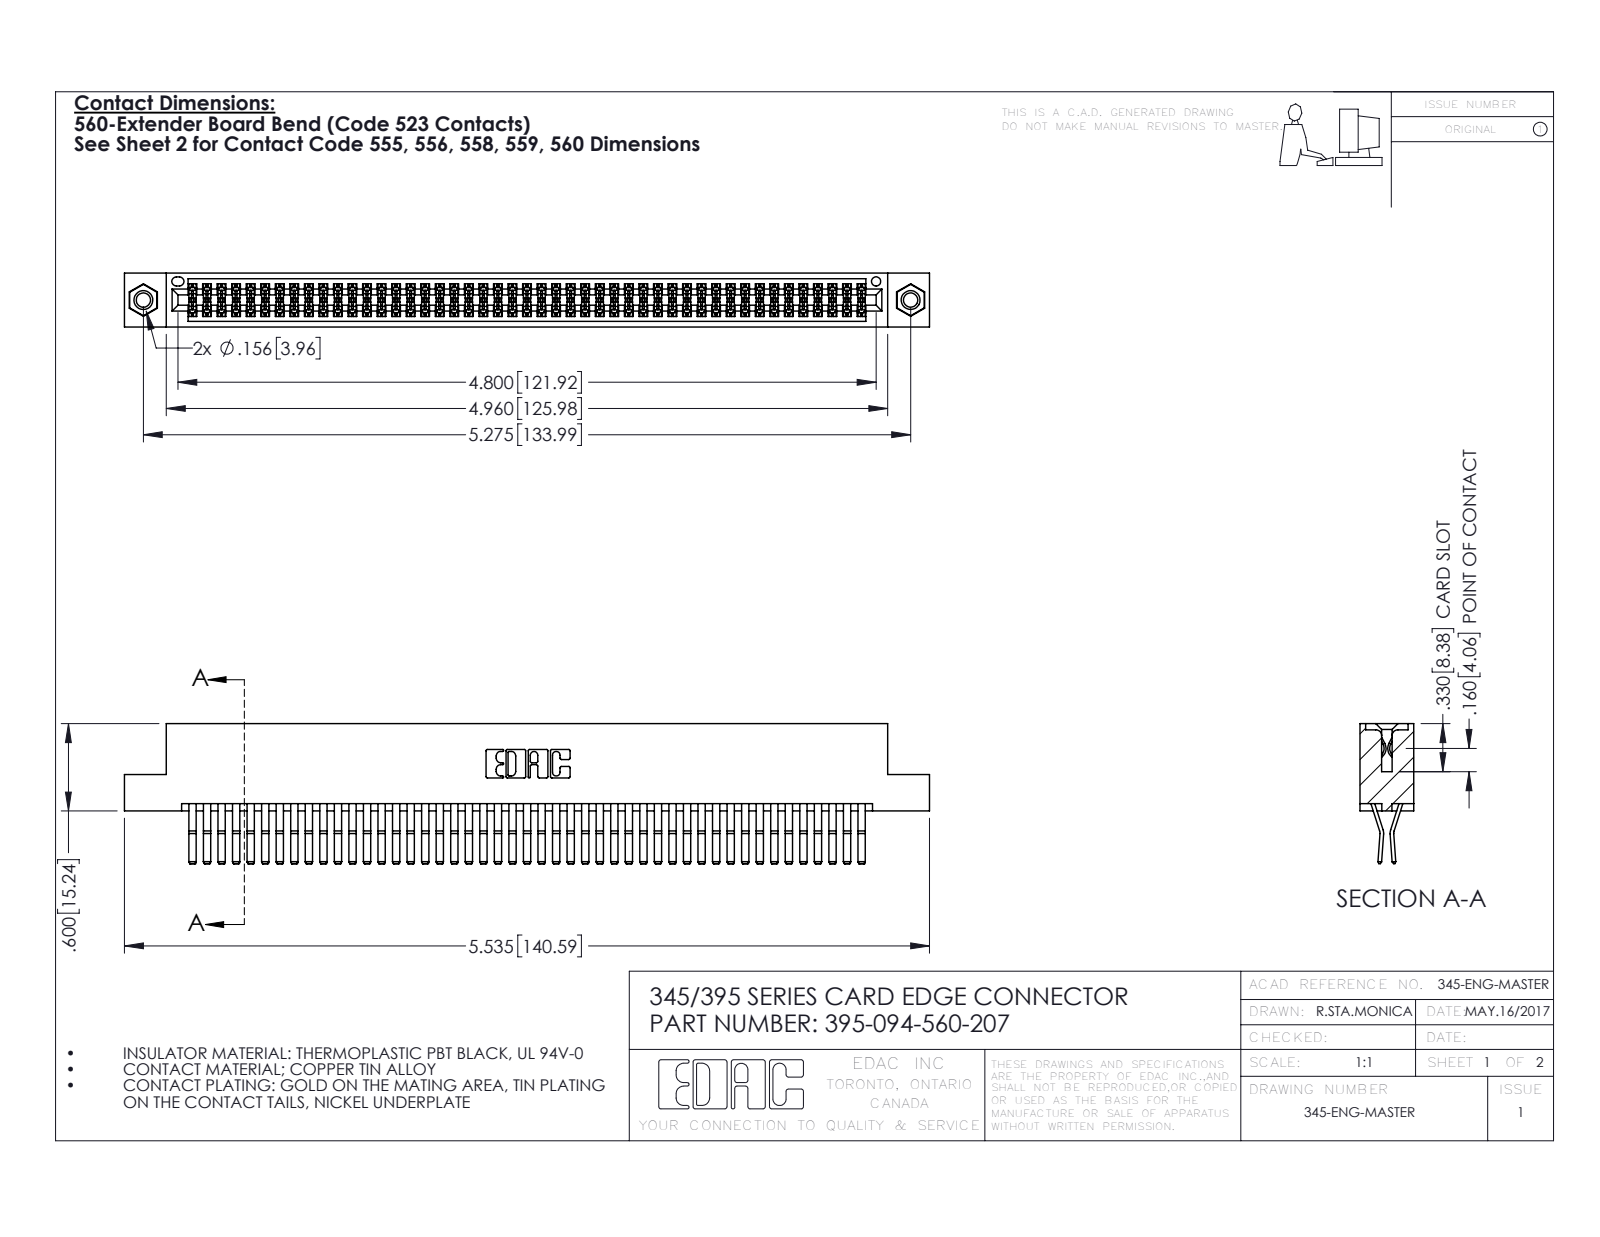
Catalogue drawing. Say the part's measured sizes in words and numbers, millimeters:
The part is named "395-094-560-207; 345-292-001_560 Tail; 345-250-001_345-250-005-103; 345 Part_Flush Mounting Lugs - 0.156 Dia-TI". Its 3-D file was written by "SolidWorks 2016 (CONFIG_CONTROL_DESIGN)". It is 97 solids with 5074 faces: 3214 planar, 1844 cylindrical and 16 other. Overall it measures 140.6 by 24.4 by 9.4 millimeters. Its volume is 14 300 cubic millimeters and its surface area 22 860 square millimeters. Round holes: 2 of diameter 2.5, 2 of diameter 3.2, 2 of diameter 4, 1 of diameter 1.6. Round bosses or shafts: 2 of diameter 3.9. Partial cylindrical surfaces (rounded edges, fillets, slot ends): 141 of radius 0.2, 22 of radius 0.3, 6 of radius 0.2, 6 of radius 0.8, 3 of radius 0.7, 2 of radius 0.3, 2 of radius 0.4, 2 of radius 0.5. The main face-to-face distances are 0.6, 1.8, 7.6, 5.1, 9.4, 2.5, 6.9, 5.7, 4.4, 3.8. The hole center spacings are 6.9, 128, 134.
